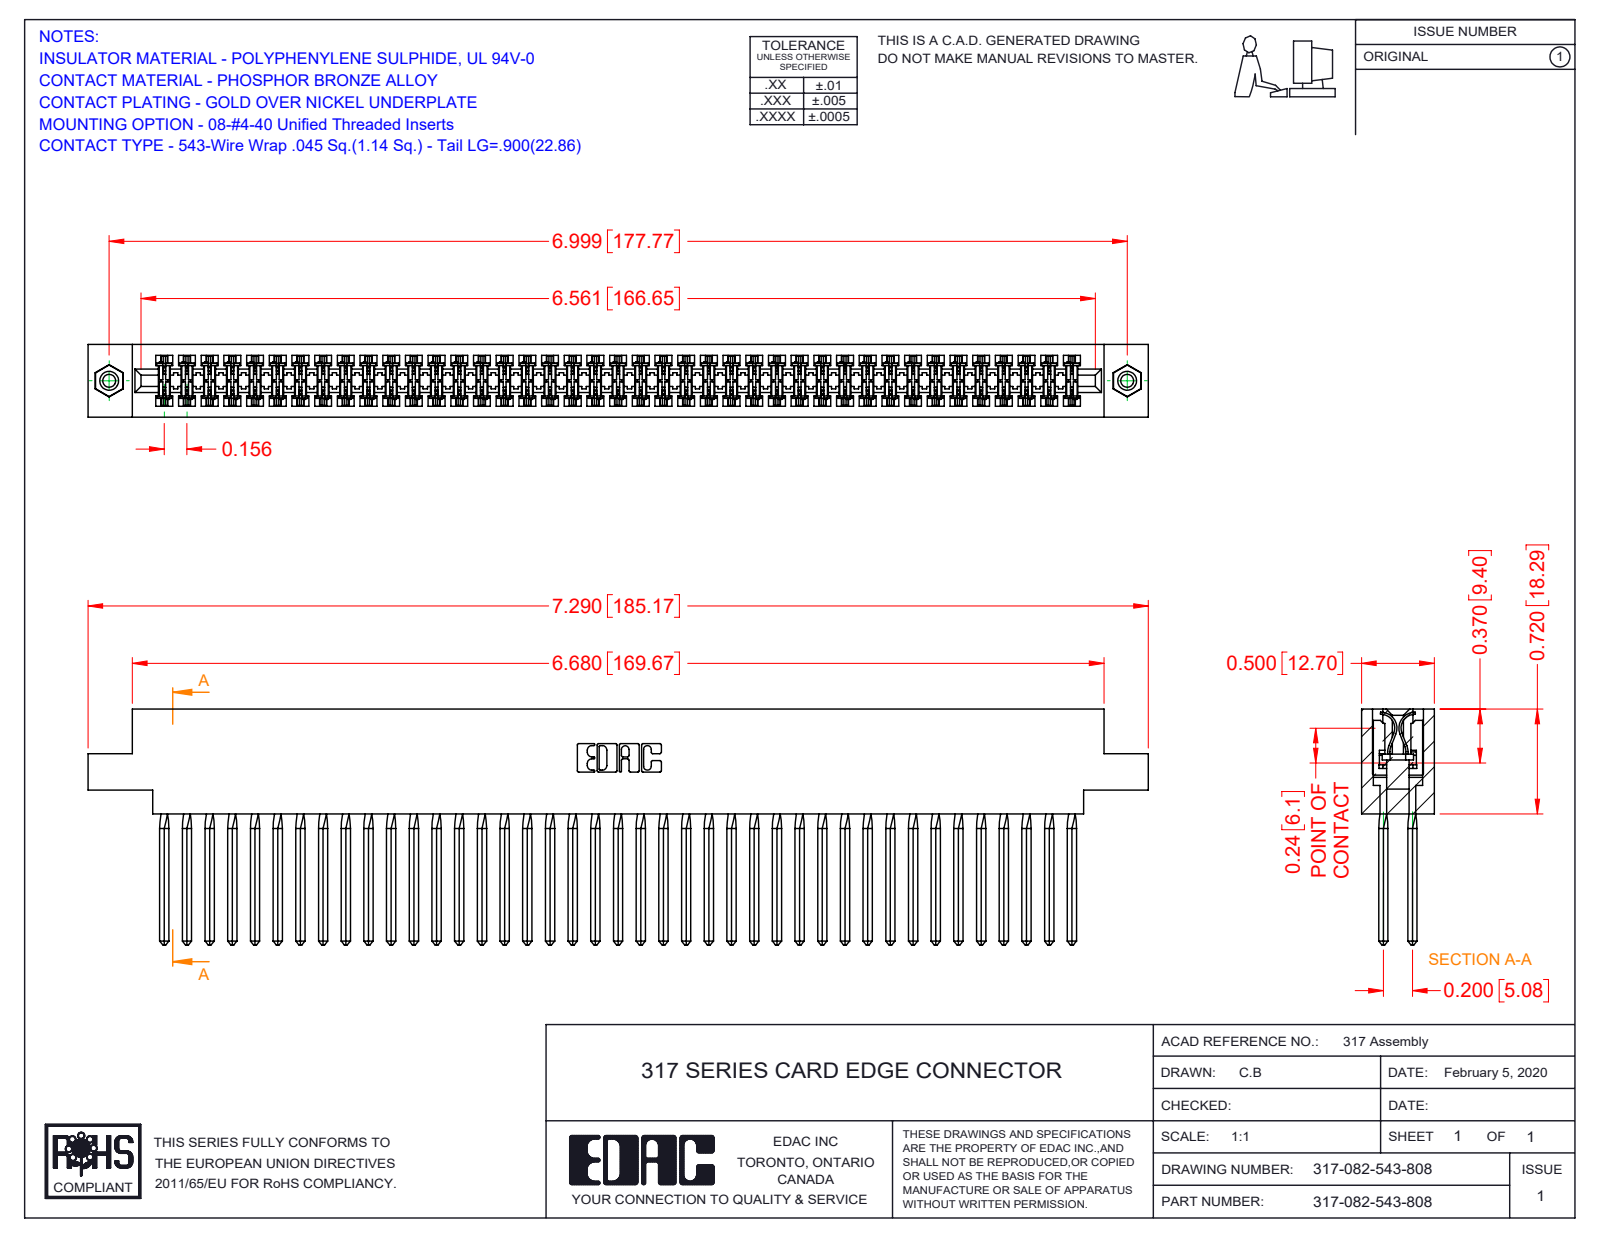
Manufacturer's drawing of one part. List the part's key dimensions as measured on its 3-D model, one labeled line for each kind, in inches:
Part name (STEP PRODUCT): 317 Part_.156 Dia - TI; 345-250-001_345-250-003-102; 317-082-543-808; 317-290-001_543
STEP written by: SolidWorks 2016 (CONFIG_CONTROL_DESIGN)
Units: inches
Bodies: 85 solids, 7460 faces (6076 planar, 1040 cylindrical, 344 other)
Overall size (bounding box): 7.29 × 1.62 × 0.5
Volume: 1.919 in³ · Surface area: 73.91 in²
Round holes (diameter × count): ⌀0.089 ×2, ⌀0.125 ×2, ⌀0.156 ×2
Round bosses / shafts (diameter × count): ⌀0.155 ×2
Partial cylindrical surfaces — rounded edges, fillets, slot ends (radius × count): R0.015 ×164, R0.01 ×22, R0.007 ×6, R0.031 ×6, R0.026 ×3, R0.095 ×2, R0.1 ×2, R0.11 ×2
Main face-to-face distances: 0.5, 0.075, 0.425, 0.35, 0.195, 0.11, 0.094, 0.2, 0.115, 0.131
Hole centre spacings: 6.999
